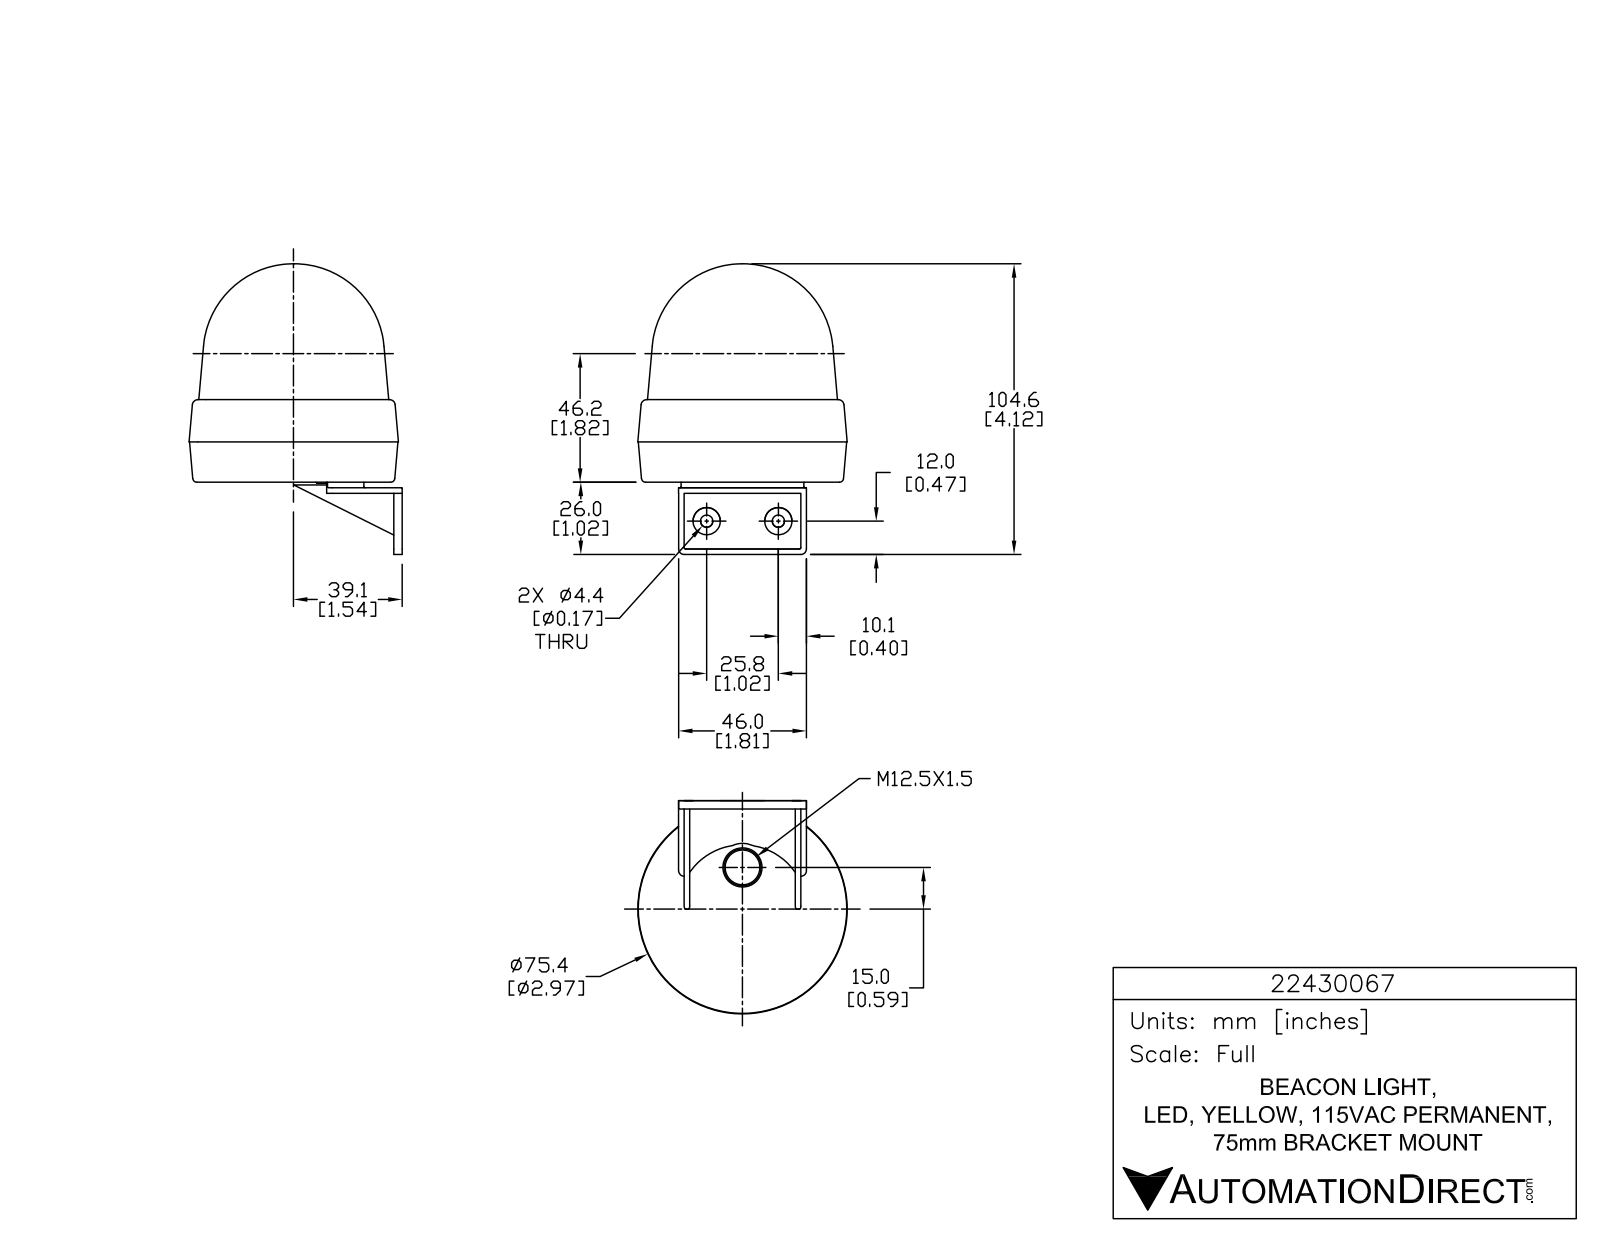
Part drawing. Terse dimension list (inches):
name: 22430067
written by: SolidWorks 2015 (AUTOMOTIVE_DESIGN)
unit: in
bodies: 1 solid, 819 faces (549 planar, 180 cylindrical, 90 other)
size: 4.117 × 3.253 × 2.967
volume: 16.02 in³; area: 41.97 in²
holes: 3× ⌀0.059, 2× ⌀0.173
bosses: 3× ⌀0.339, 3× ⌀0.084, 2× ⌀0.386
rounds: 9× R0.005, 6× R0.005, 6× R0.012, 6× R0.012, 6× R0.012, 6× R0.02, 6× R0.196, 4× R0.079
face distances: 0.079, 0.157, 1.574, 0.039, 0.118, 1.653, 1.496, 0.079, 1.654, 1.732
hole spacings: 1.016
